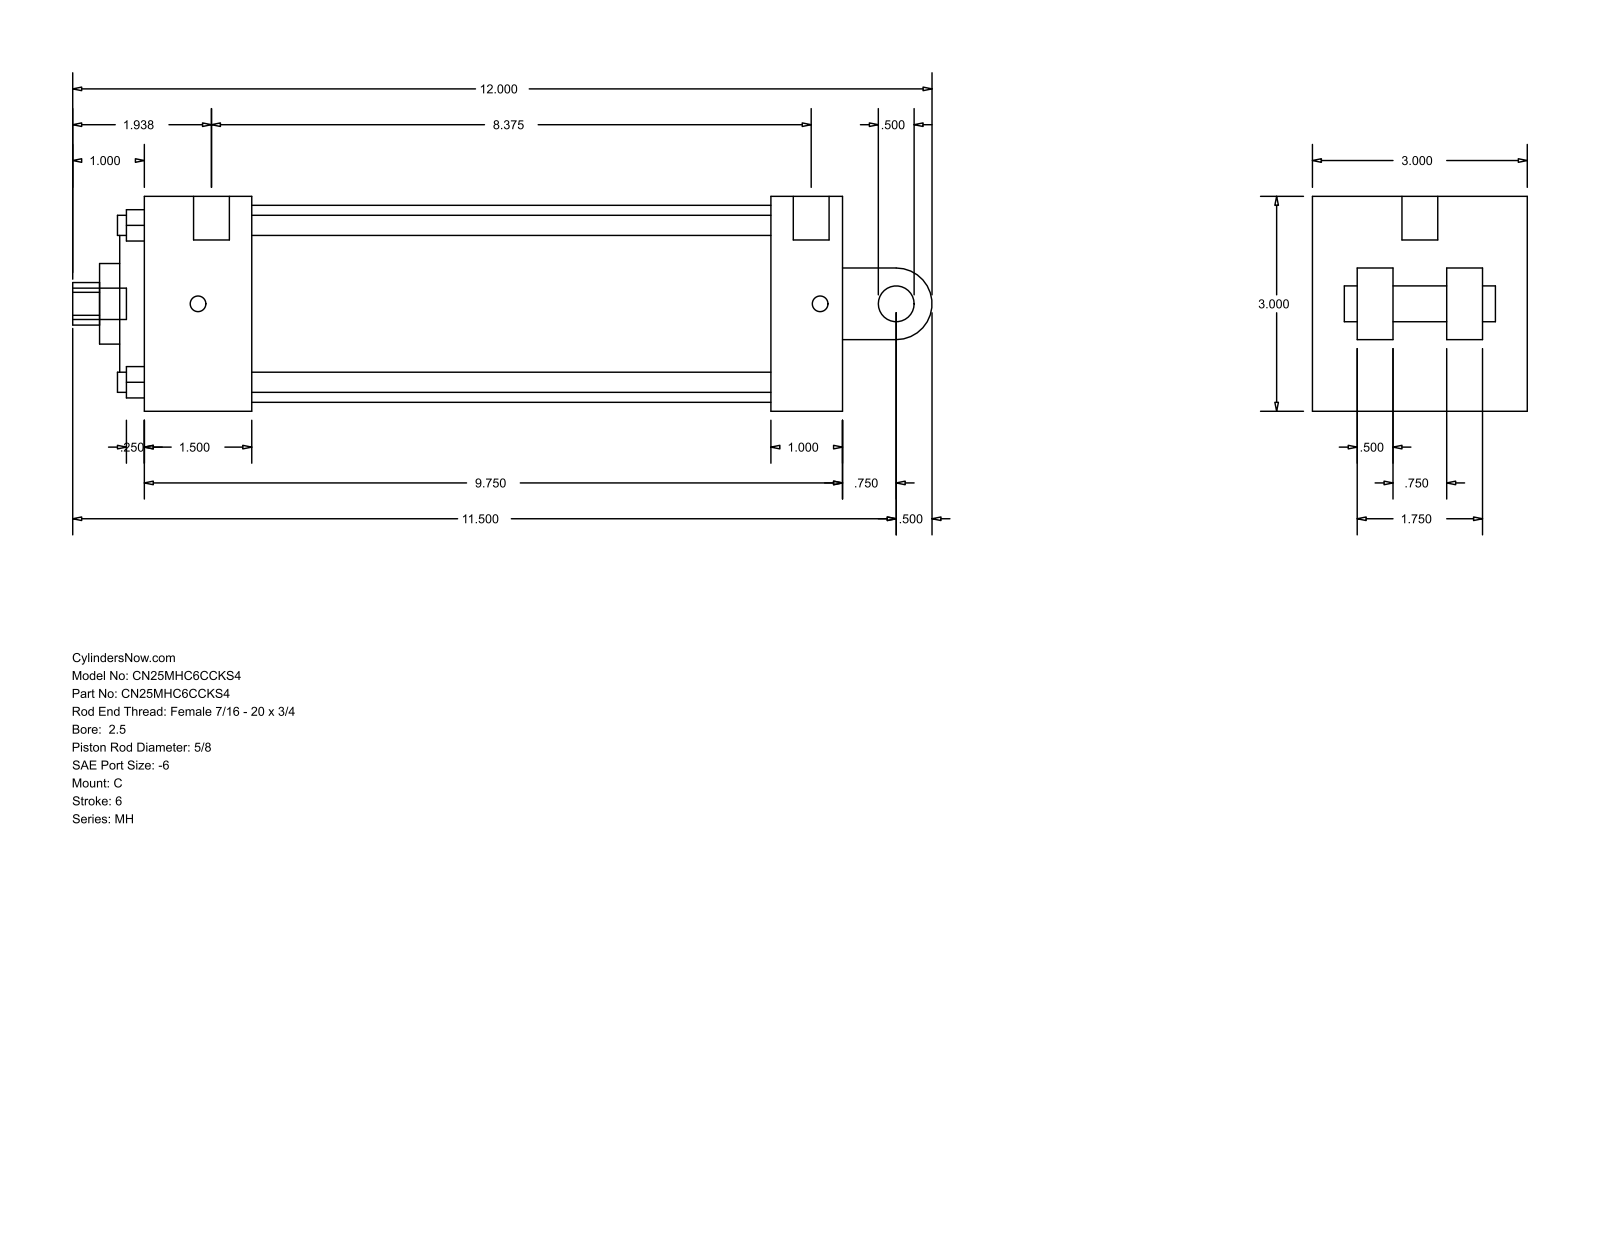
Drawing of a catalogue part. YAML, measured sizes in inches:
part_name: "MH_C__0250_0.625"
step_written_by: "GSSL Pune (CONFIG_CONTROL_DESIGN)"
units: inches
bodies: {solids: 0, faces: 101, planar: 71, cylindrical: 30, other: 0}
overall_size: [12, 3, 3]
round_holes:
  - {diameter: 0.281, count: 4}
  - {diameter: 0.219, count: 2}
  - {diameter: 0.5, count: 1}
  - {diameter: 0.625, count: 1}
  - {diameter: 1.125, count: 1}
  - {diameter: 2.187, count: 1}
  - {diameter: 2.75, count: 1}
round_bosses_or_shafts:
  - {diameter: 0.5, count: 2}
  - {diameter: 0.219, count: 2}
  - {diameter: 0.437, count: 1}
partial_cylinders:
  - {radius: 0.297, count: 1}
  - {radius: 0.5, count: 1}
face_to_face_distances: [3, 1, 9.75, 0.625, 8.75, 1.5, 7.25, 8.25, 0.344, 1.844]
hole_center_spacings: [1.548, 2.19, 3.097, 0.125]
